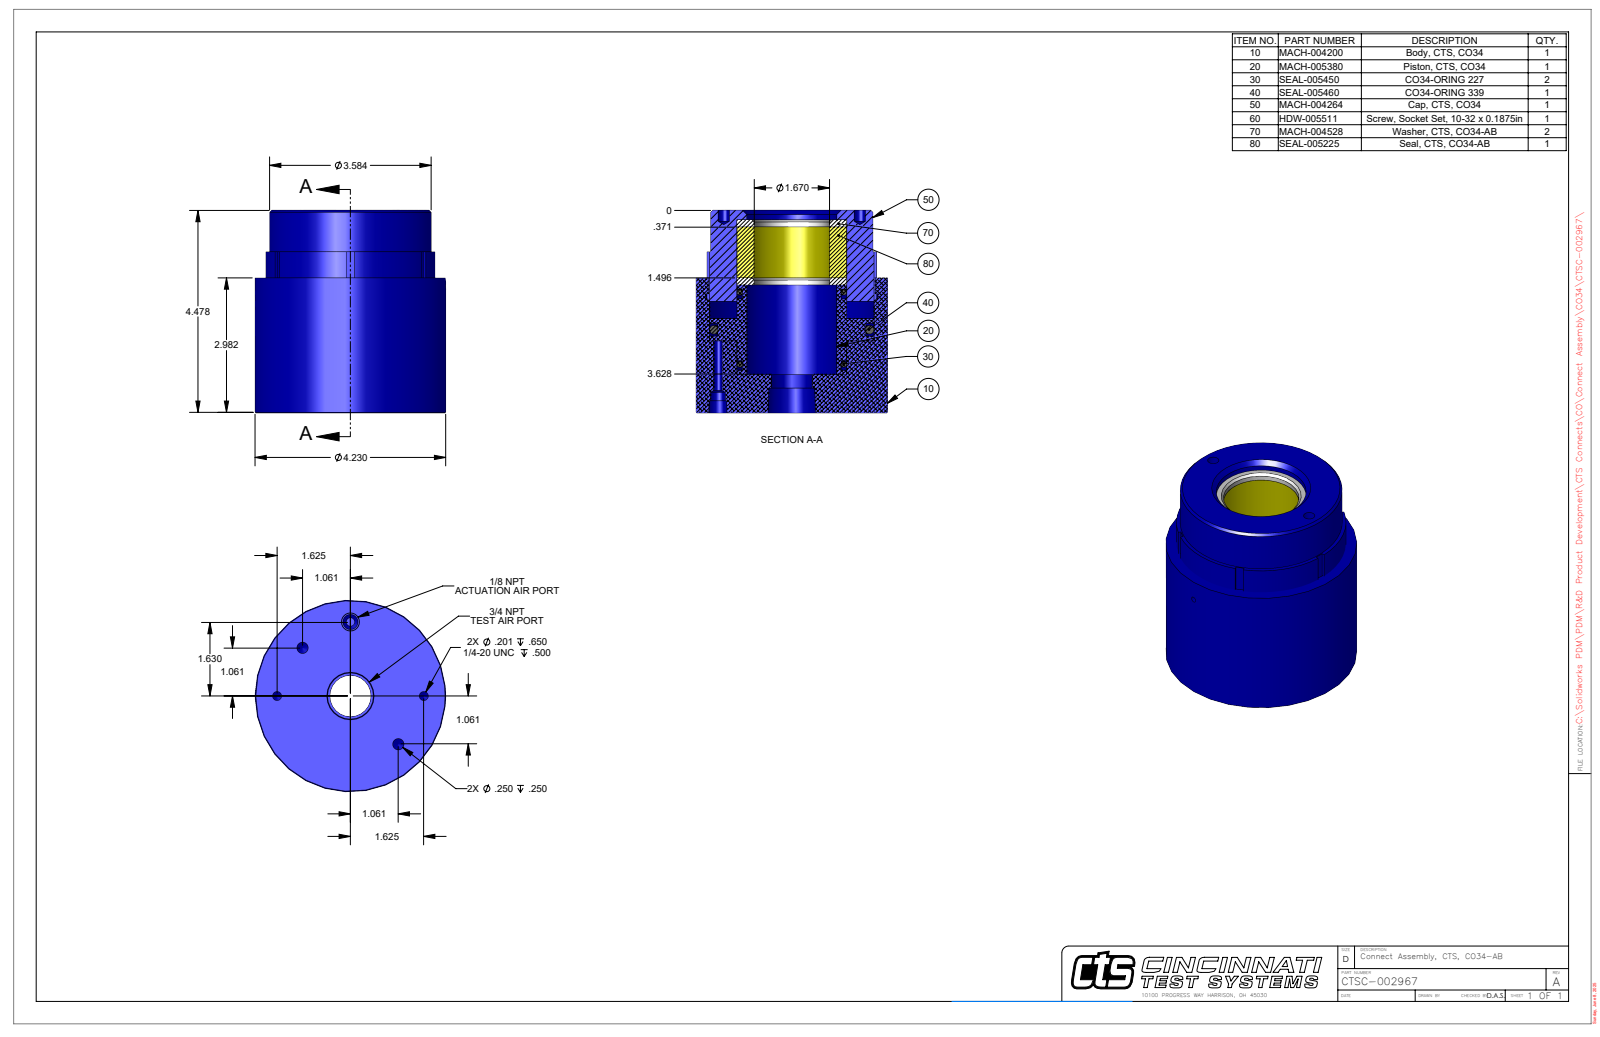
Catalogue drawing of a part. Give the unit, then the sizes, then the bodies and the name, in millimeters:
Units: millimetres
Overall size (bounding box): 113.7 × 107.5 × 107.4
Round holes (diameter × count): ⌀6.4 ×4, ⌀5.1 ×2, ⌀3.2 ×1, ⌀4 ×1, ⌀4.7 ×1, ⌀8.4 ×1, ⌀23 ×1, ⌀42.4 ×1, ⌀42.5 ×1, ⌀50.5 ×1, ⌀50.5 ×1, ⌀61.6 ×1
Round bosses / shafts (diameter × count): ⌀107.4 ×1, ⌀95.3 ×1, ⌀91 ×1, ⌀61.4 ×1
Partial cylindrical surfaces — rounded edges, fillets, slot ends (radius × count): R46.8 ×1, R53.1 ×1
Main face-to-face distances: 113.7, 75.7, 38, 21.6, 54.2, 92.2, 4, 71.8, 50.2, 42
Hole centre spacings: 38.1, 56.2, 29.2, 30.5, 41.3, 58.5, 70.4, 73.3
Volume: 765 300 mm³ · Surface area: 73 030 mm²
Bodies: 1 solid, 129 faces (47 planar, 56 cylindrical, 26 other)
Part name (STEP PRODUCT): CTSC-002967
STEP written by: SolidWorks 2023 (AUTOMOTIVE_DESIGN)
